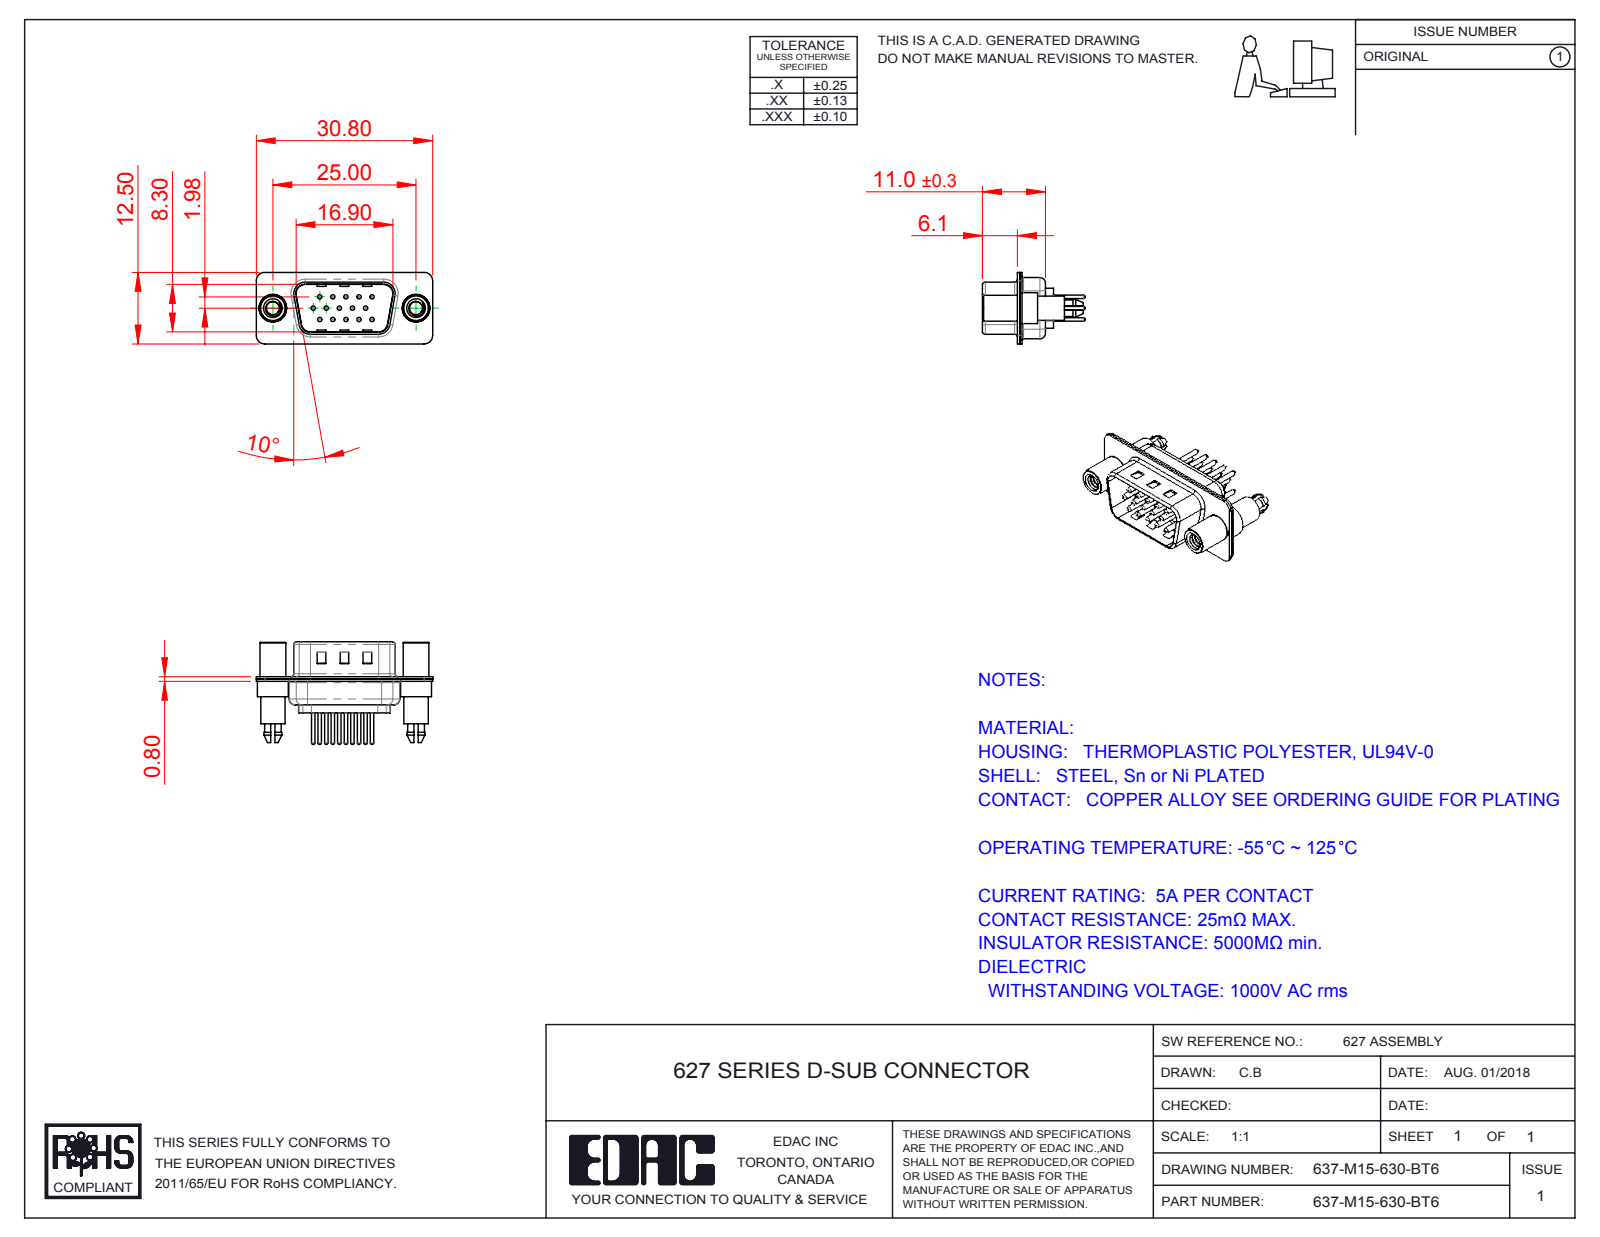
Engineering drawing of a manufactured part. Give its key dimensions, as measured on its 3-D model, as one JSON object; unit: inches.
{"part_name": "637-M15-630-BT6; 637M Contact Row 2_30; 637M Shell Rear_15 Contacts; 637M Contact Row 3_30 (+4 more)", "step_written_by": "SolidWorks 2016 (CONFIG_CONTROL_DESIGN)", "units": "inches", "bodies": {"solids": 20, "faces": 943, "planar": 250, "cylindrical": 375, "other": 318}, "overall_size": [1.213, 0.705, 0.492], "volume_in3": 0.103, "surface_area_in2": 7.093, "round_holes": [[0.03, 15], [0.063, 15], [0.079, 15], [0.089, 2], [0.157, 2], [0.189, 2]], "round_bosses_or_shafts": [[0.059, 15], [0.024, 15], [0.213, 2], [0.193, 2], [0.177, 2], [0.167, 2]], "partial_cylinders_radius": [[0.059, 18], [0.079, 12], [0.063, 10], [0.02, 8], [0.01, 4], [0.024, 4], [0.026, 4], [0.035, 4]], "face_to_face_distances": [0.016, 0.031, 0.374, 0.358, 0.026, 0.343, 0.39, 0.248, 0.03, 0.055], "hole_center_spacings": [0.156, 0.09, 0.09, 0.18, 0.238, 0.27, 0.312, 0.238]}
